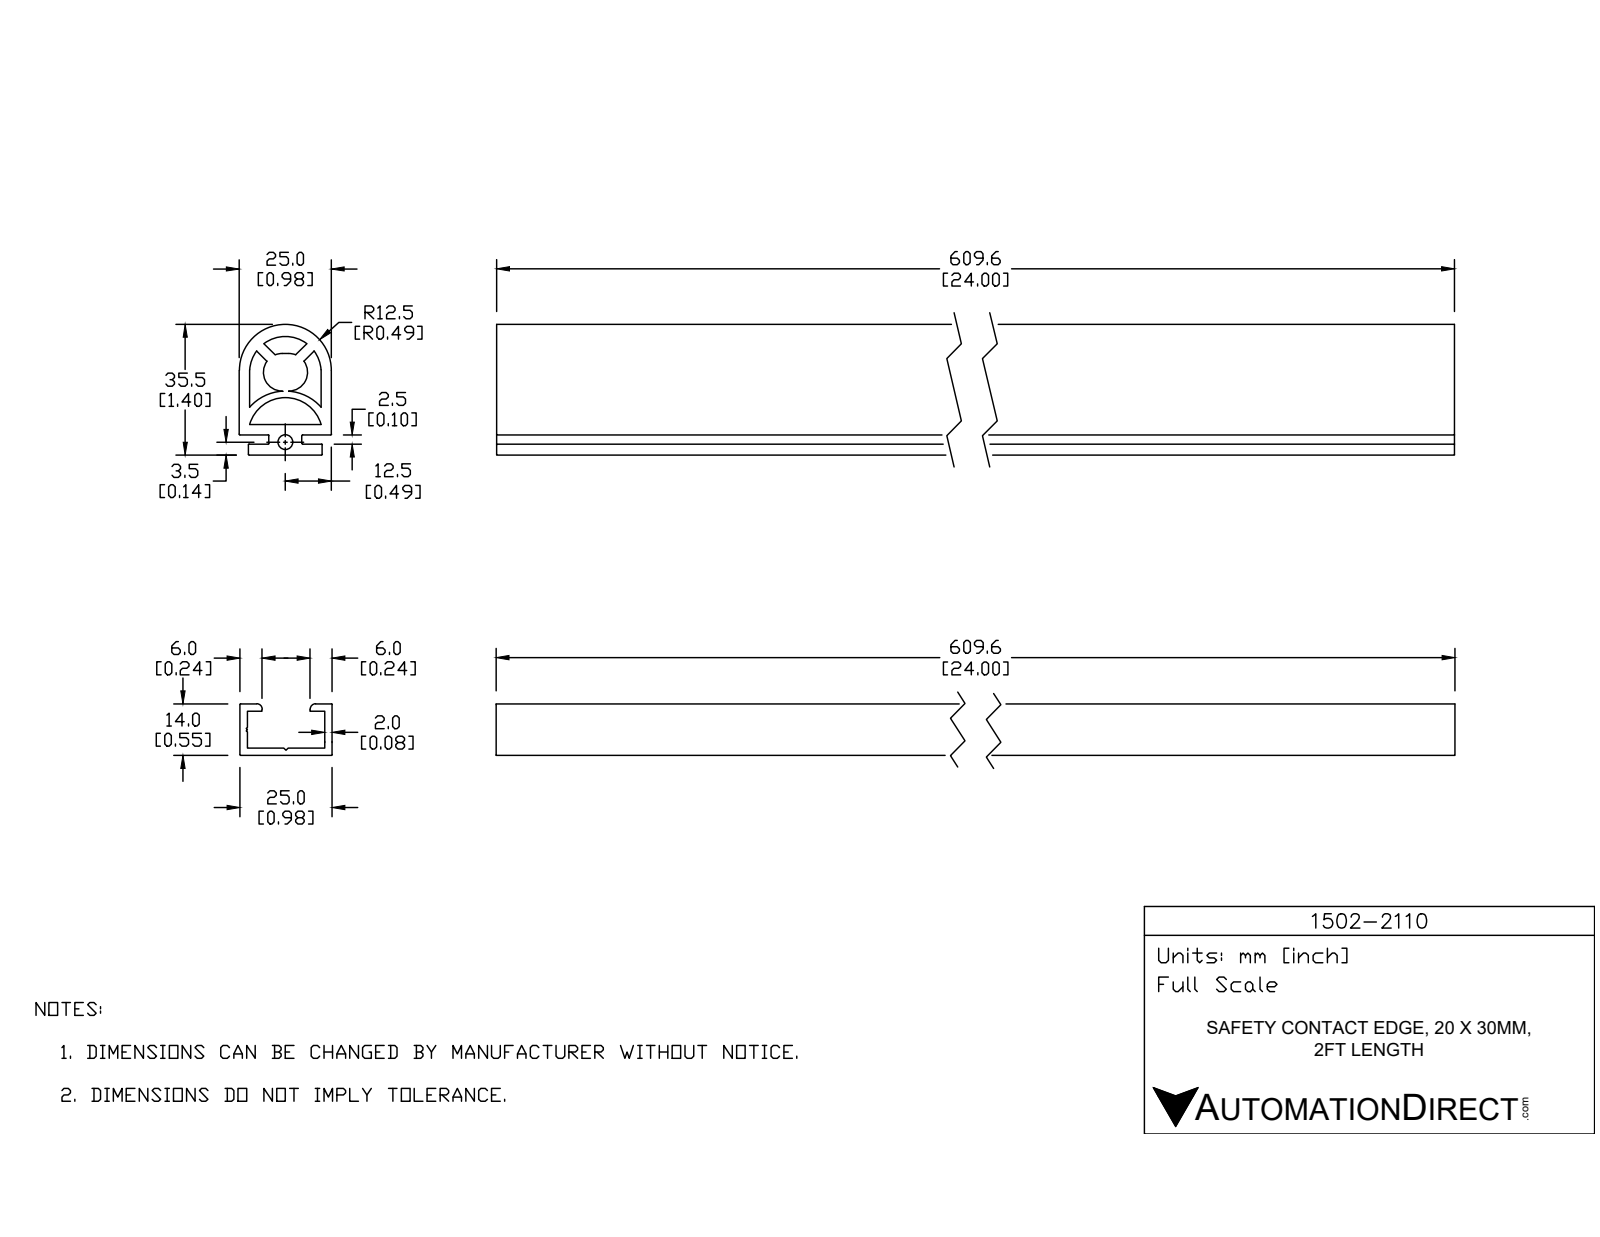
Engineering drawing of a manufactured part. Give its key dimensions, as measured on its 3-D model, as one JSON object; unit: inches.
{"part_name": "1502-2110", "step_written_by": "SolidWorks 2017 (AUTOMOTIVE_DESIGN)", "units": "inches", "bodies": {"solids": 1, "faces": 25, "planar": 13, "cylindrical": 12, "other": 0}, "overall_size": [24, 1.398, 0.984], "volume_in3": 28.01, "surface_area_in2": 138.4, "round_holes": [[0.157, 1]], "partial_cylinders_radius": [[0.008, 10], [0.492, 1]], "face_to_face_distances": [0.217, 0.984, 0.098, 0.118, 0.886, 0.315, 0.669, 0.571, 0.787, 0.354]}
